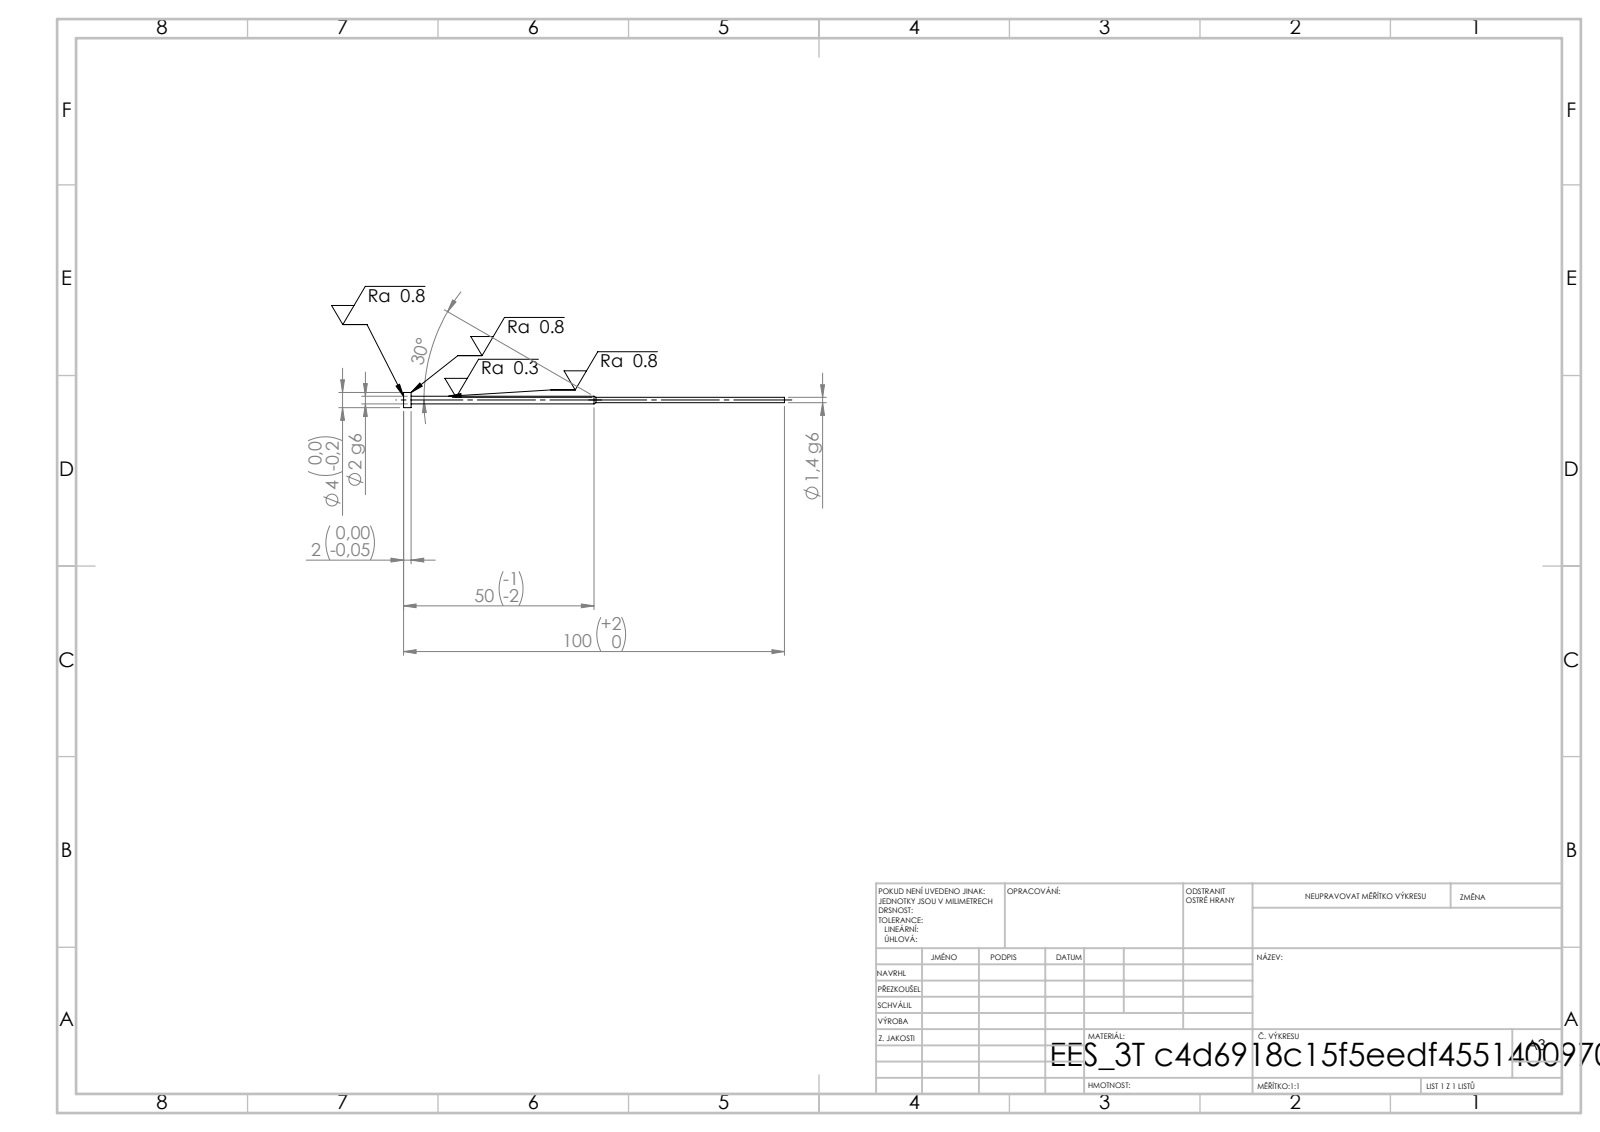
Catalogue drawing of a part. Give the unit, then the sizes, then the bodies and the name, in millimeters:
Units: millimetres
Overall size (bounding box): 100 × 4 × 4
Round bosses / shafts (diameter × count): ⌀4 ×1, ⌀2 ×1, ⌀1.4 ×1
Main face-to-face distances: 2, 98, 100
Volume: 253 mm³ · Surface area: 571 mm²
Bodies: 1 solid, 11 faces (3 planar, 6 cylindrical, 2 other)
STEP written by: SolidWorks 2019 (CONFIG_CONTROL_DESIGN)
